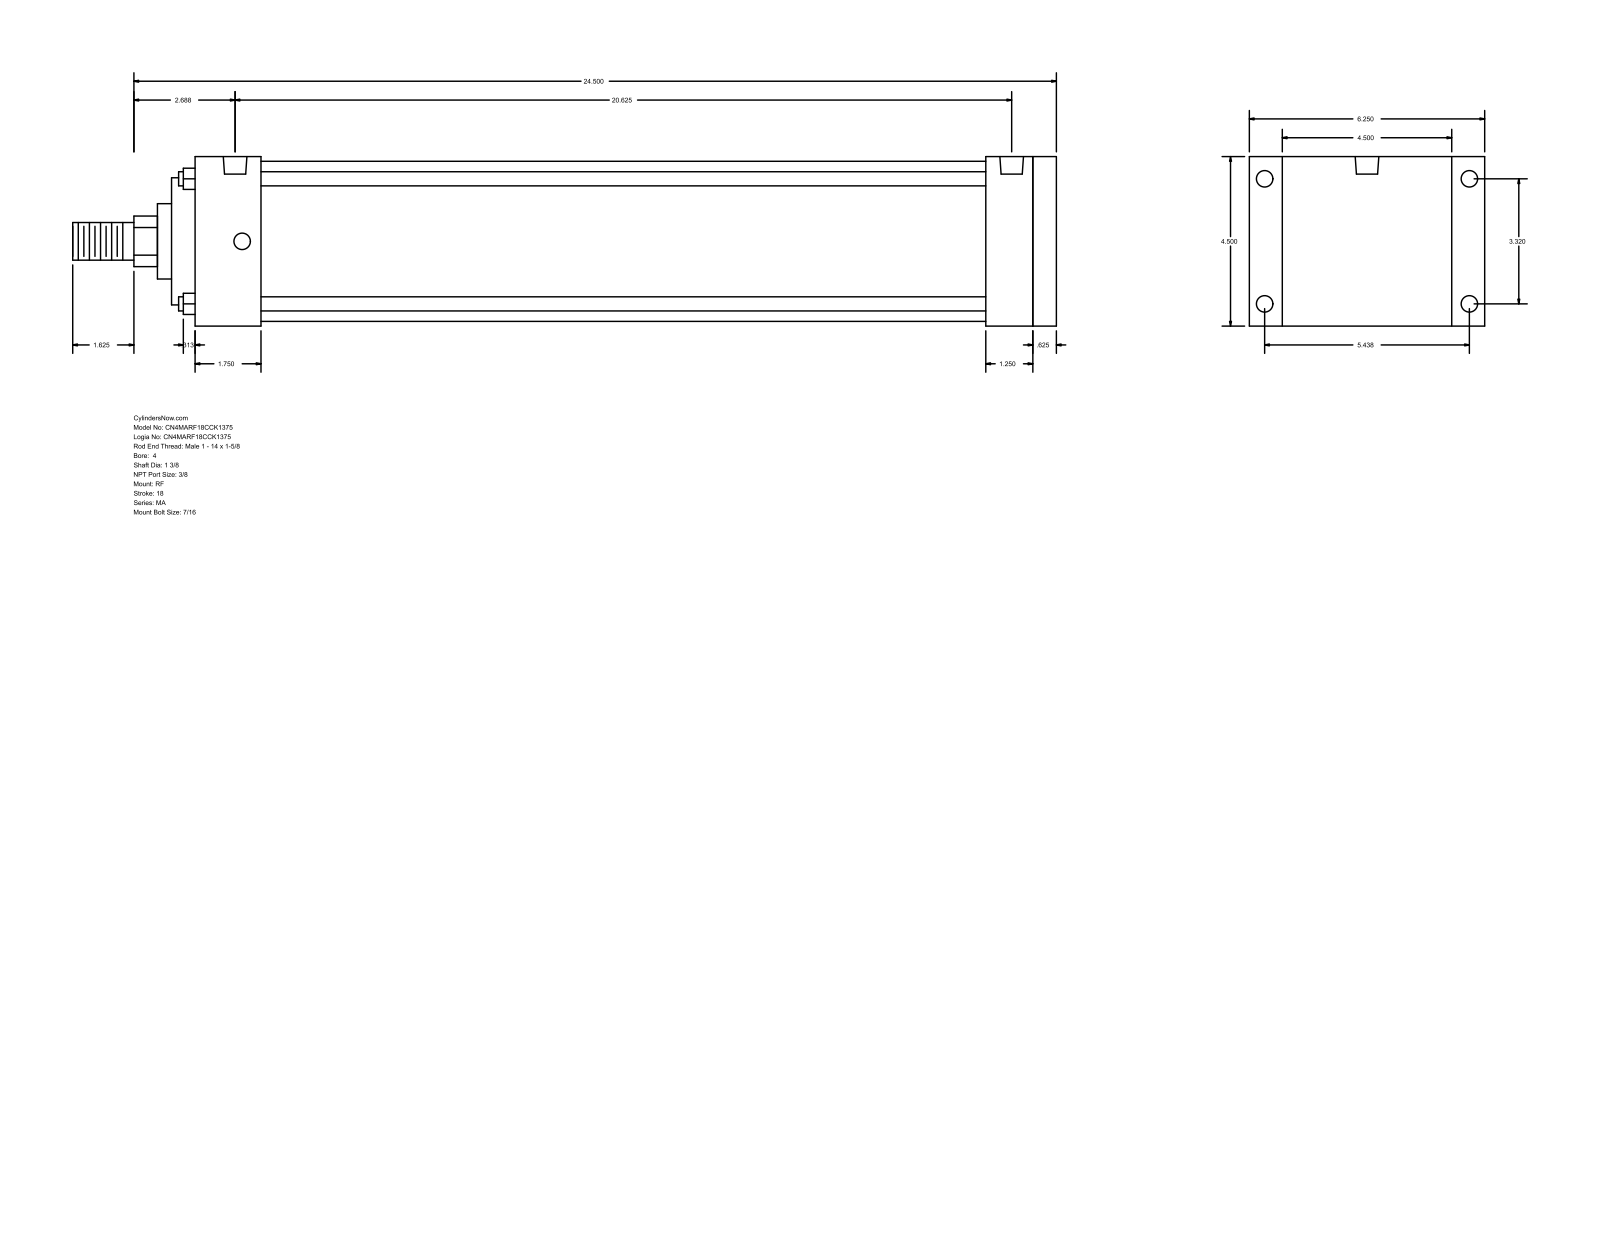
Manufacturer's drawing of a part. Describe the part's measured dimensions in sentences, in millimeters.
The part is named "MA_RF__0400_1.375". Its 3-D file was written by "GSSL Pune (CONFIG_CONTROL_DESIGN)". It is 0 solids with 94 faces: 65 planar, 29 cylindrical and 0 other. Overall it measures 663.58 by 158.75 by 114.3 millimeters. Round holes: 8 of diameter 11.11, 2 of diameter 15.93. Round bosses or shafts: 4 of diameter 9.53, 1 of diameter 107.95, 1 of diameter 85.72, 1 of diameter 50.8, 1 of diameter 34.92, 1 of diameter 25.4. Partial cylindrical surfaces (rounded edges, fillets, slot ends): 1 of radius 17.06. The main face-to-face distances are 114.3, 581.03, 15.88, 565.15, 15.87, 581.02, 596.9, 22.23, 136.53, 549.27. The hole center spacings are 84.32, 138.12, 161.82, 514.35, 4.76, 4.77, 519.11, 519.12.
